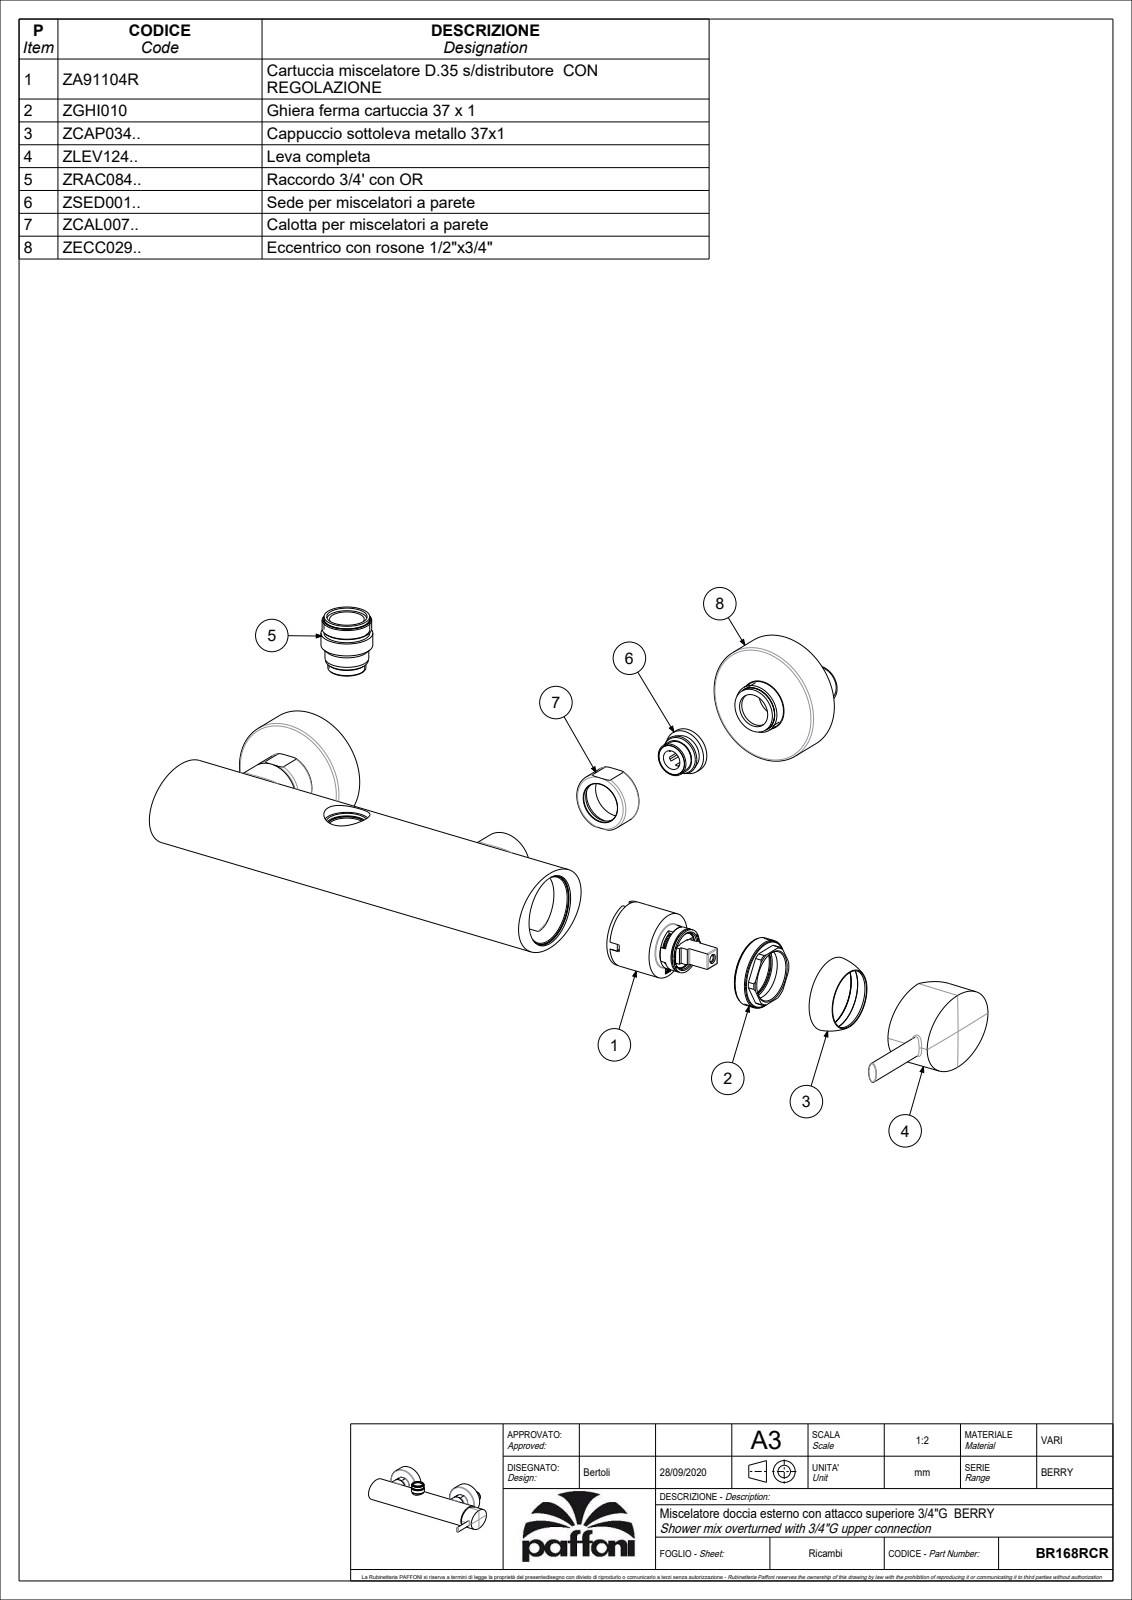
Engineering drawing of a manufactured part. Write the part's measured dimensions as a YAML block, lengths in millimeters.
part_name: "BR168RCR"
step_written_by: "CREO PARAMETRIC BY PTC INC, 2020044 (CONFIG_CONTROL_DESIGN)"
units: millimeters
bodies: {solids: 1, faces: 1365, planar: 712, cylindrical: 340, other: 313}
overall_size: [263.25, 141.5, 72.35]
volume: 274618
surface_area: 161399
round_holes:
  - {diameter: 10.5, count: 3}
  - {diameter: 4, count: 2}
  - {diameter: 7, count: 2}
  - {diameter: 16.5, count: 2}
  - {diameter: 18, count: 2}
  - {diameter: 21.6, count: 2}
  - {diameter: 23.2, count: 2}
  - {diameter: 24.5, count: 2}
  - {diameter: 25, count: 2}
  - {diameter: 62.3, count: 2}
  - {diameter: 3, count: 1}
  - {diameter: 3.3, count: 1}
round_bosses_or_shafts:
  - {diameter: 24, count: 3}
  - {diameter: 63.5, count: 2}
  - {diameter: 31.2, count: 2}
  - {diameter: 27, count: 2}
  - {diameter: 35.5, count: 1}
  - {diameter: 35, count: 1}
  - {diameter: 34.8, count: 1}
  - {diameter: 32.2, count: 1}
partial_cylinders:
  - {radius: 0.5, count: 27}
  - {radius: 1.5, count: 14}
  - {radius: 0.15, count: 11}
  - {radius: 0.3, count: 4}
  - {radius: 1.25, count: 4}
  - {radius: 1, count: 3}
  - {radius: 4, count: 1}
  - {radius: 7, count: 1}
face_to_face_distances: [0.6, 40, 39.4, 36.5, 3.5, 35.9, 17, 5.5, 260.7, 10]
hole_center_spacings: [4.75, 7.63, 8.06, 8.2, 8.6, 9, 11.72, 12]
